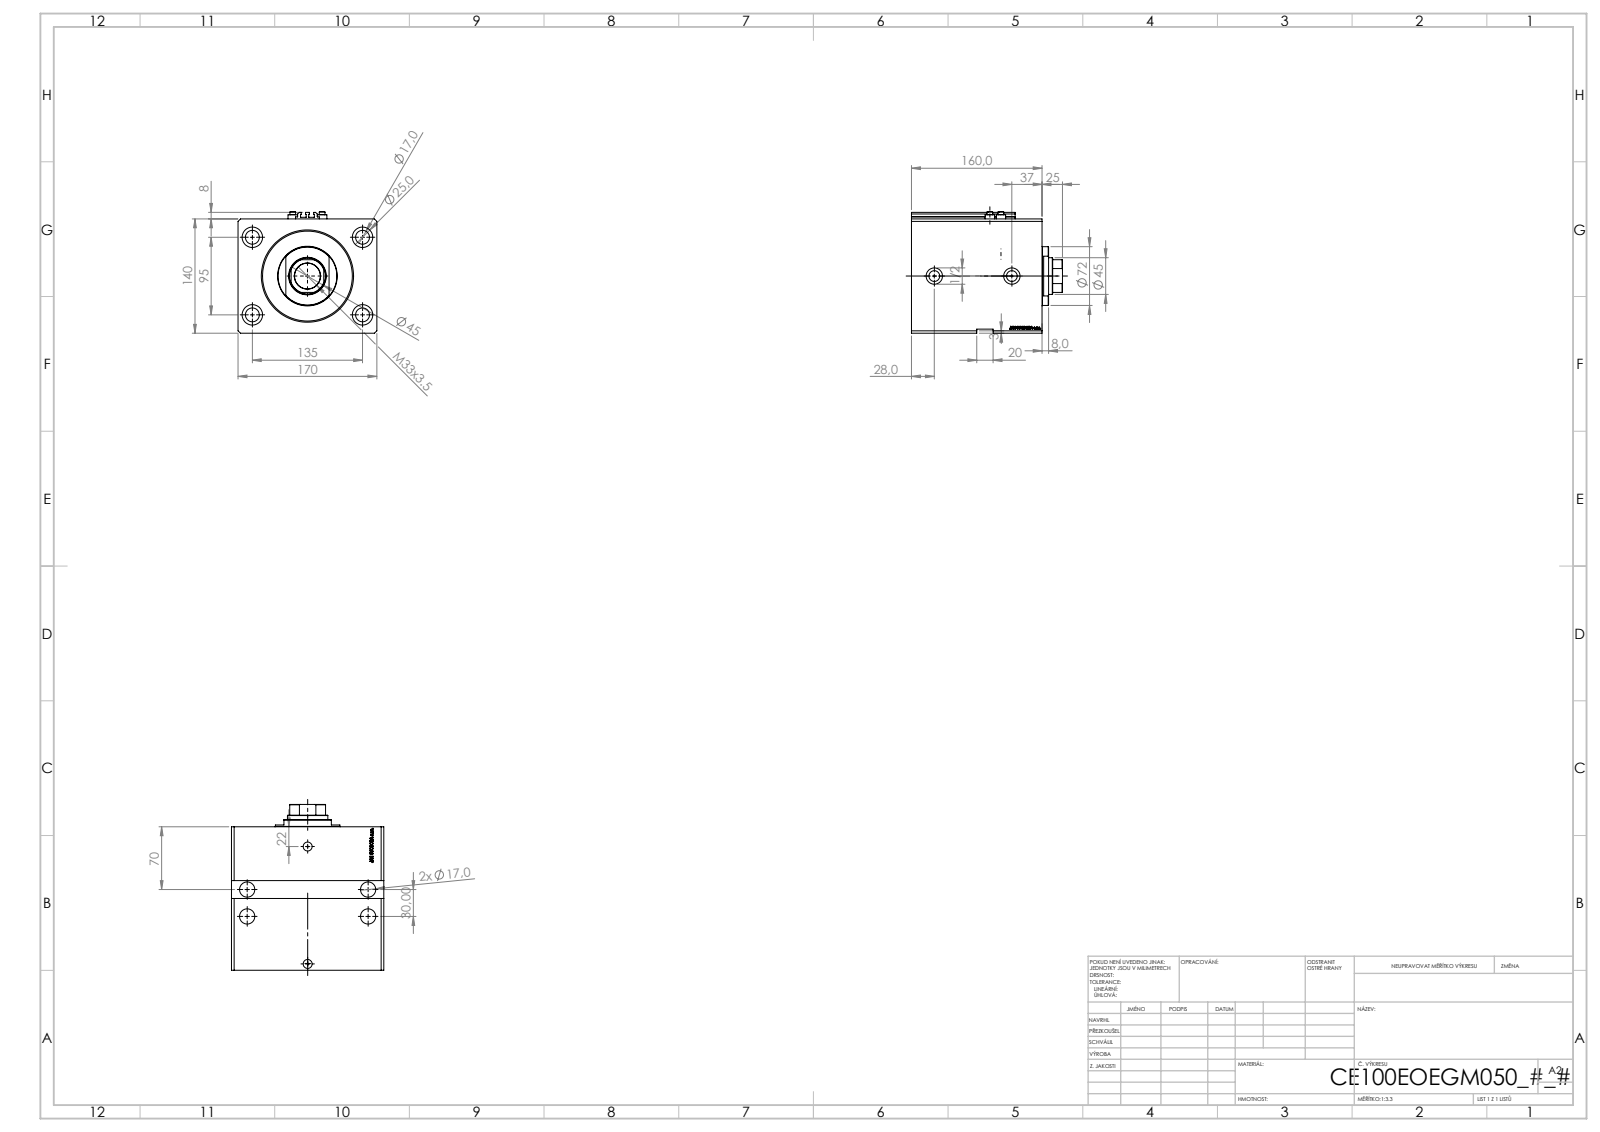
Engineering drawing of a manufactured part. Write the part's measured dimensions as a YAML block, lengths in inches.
part_name: "V250CE_C_VCP; V250CE_E_Body; V250CE_VC_E; ALLEN BOLT V250CE"
step_written_by: "SolidWorks 2019 (CONFIG_CONTROL_DESIGN)"
units: inches
bodies: {solids: 8, faces: 1123, planar: 547, cylindrical: 138, other: 438}
overall_size: [7.283, 6.693, 5.866]
volume: 197.1
surface_area: 533.2
round_holes:
  - {diameter: 0.669, count: 8}
  - {diameter: 0.049, count: 4}
  - {diameter: 0.157, count: 4}
  - {diameter: 0.984, count: 4}
  - {diameter: 0.394, count: 2}
  - {diameter: 0.518, count: 2}
  - {diameter: 0.787, count: 2}
  - {diameter: 1.24, count: 1}
  - {diameter: 1.772, count: 1}
  - {diameter: 3.937, count: 1}
  - {diameter: 4.449, count: 1}
round_bosses_or_shafts:
  - {diameter: 0.457, count: 4}
  - {diameter: 0.276, count: 4}
  - {diameter: 2.835, count: 1}
partial_cylinders:
  - {radius: 0.008, count: 10}
  - {radius: 0.866, count: 1}
face_to_face_distances: [5.512, 6.693, 6.299, 1.138, 5.161, 5.315, 0.984, 4.177, 1.969, 3.346]
hole_center_spacings: [3.25, 5.315, 3.74, 0.535, 1.181, 1.324, 1.417, 1.515]
